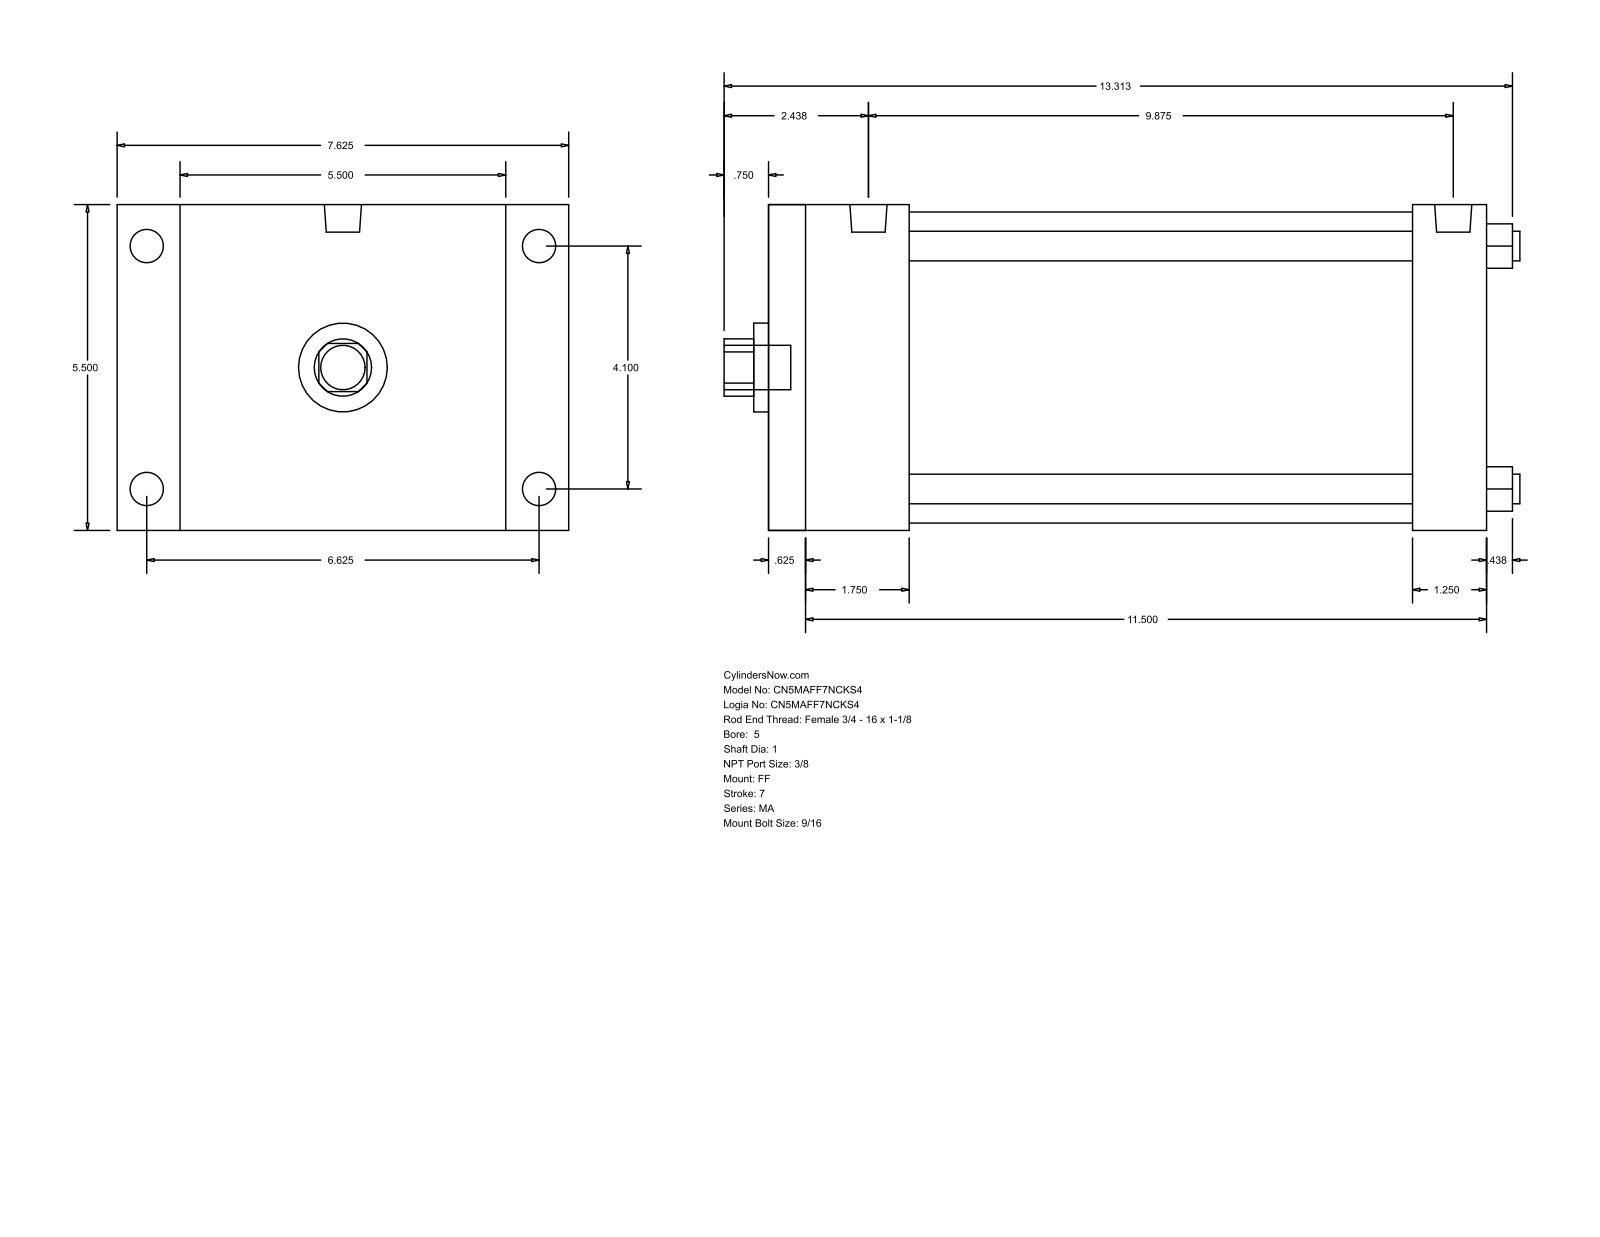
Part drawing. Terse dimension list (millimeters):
name: MA_FF__0500_1
written by: GSSL Pune (CONFIG_CONTROL_DESIGN)
unit: mm
bodies: 0 solids, 92 faces (64 planar, 28 cylindrical, 0 other)
size: 341.31 × 193.68 × 139.7
holes: 4× ⌀12.7, 1× ⌀25.4, 1× ⌀38.1, 1× ⌀133.35
bosses: 4× ⌀14.29, 4× ⌀11.11, 2× ⌀15.93, 1× ⌀19.05
rounds: 1× R12.29
face distances: 139.7, 307.97, 15.87, 292.1, 276.22, 260.35, 31.75, 60.33, 44.46, 215.89
hole spacings: 73.64, 104.14, 147.28
